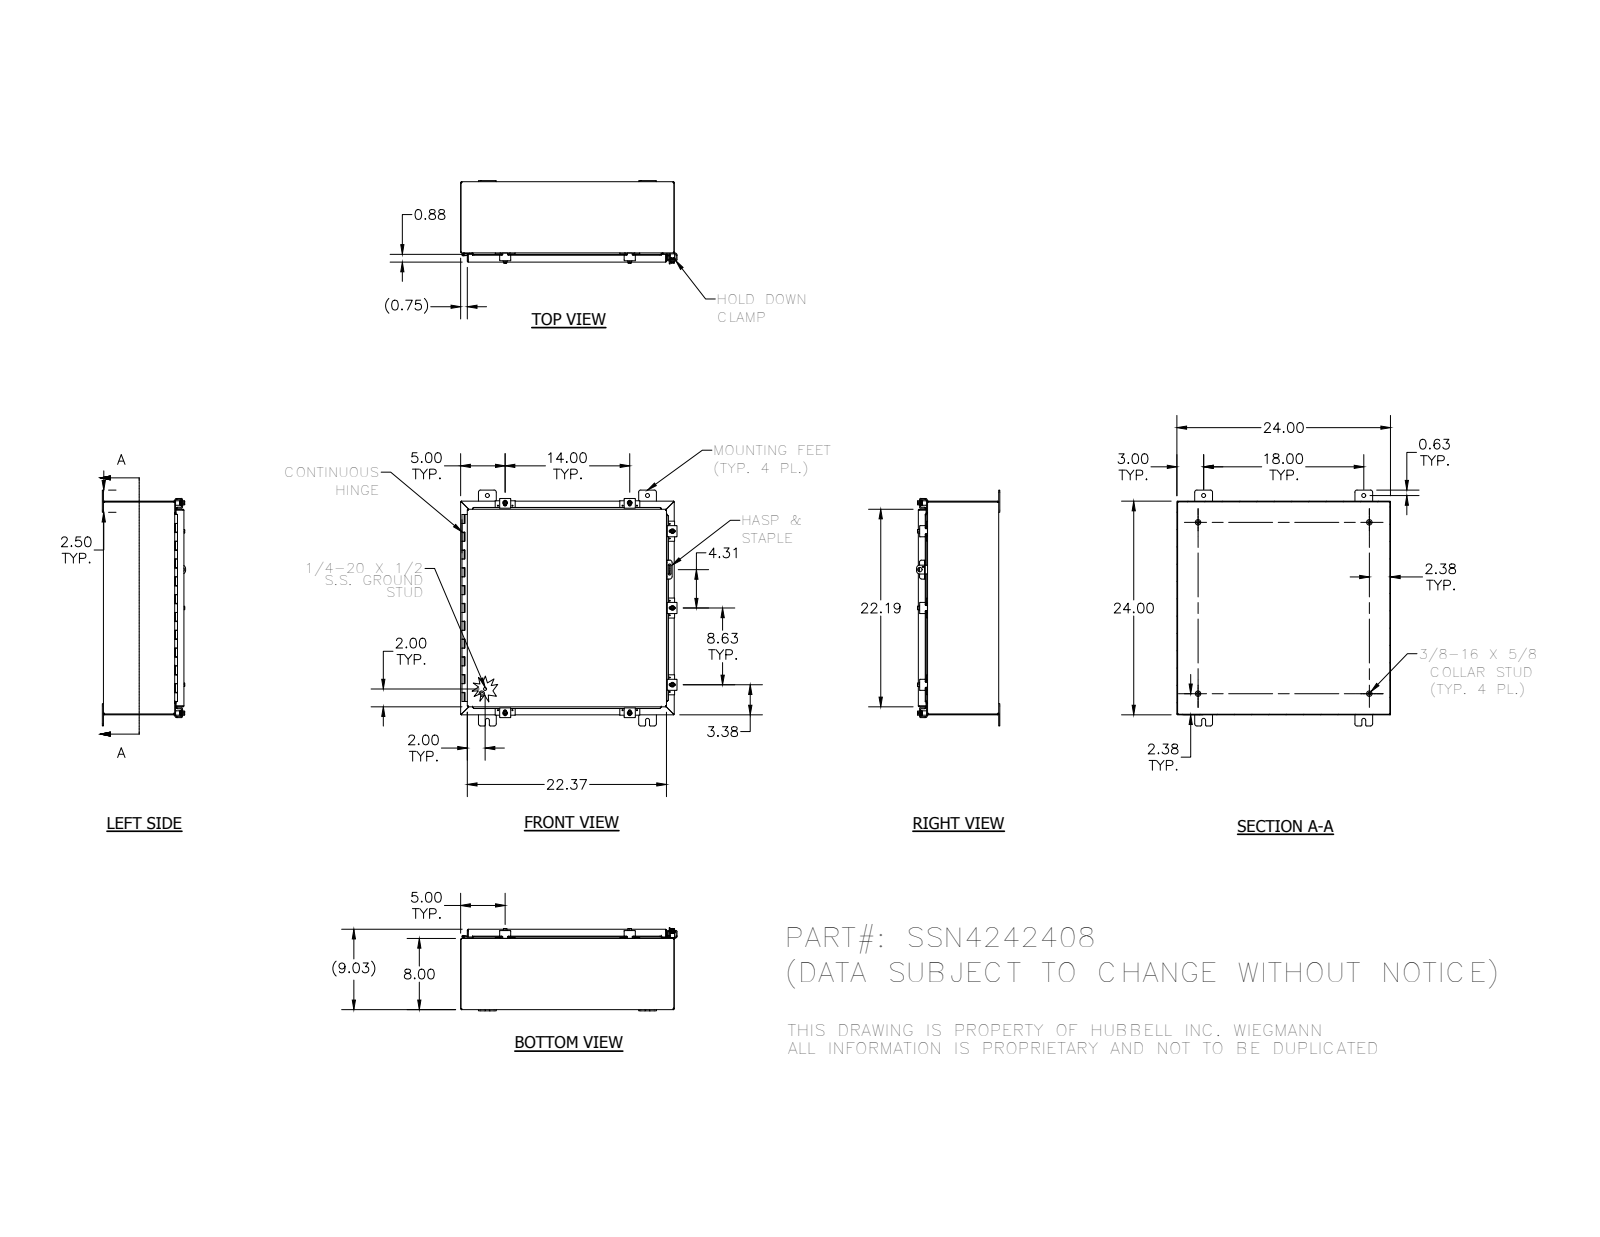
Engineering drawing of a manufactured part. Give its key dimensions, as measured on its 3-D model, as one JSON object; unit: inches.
{"part_name": "30824; 30824-1; 38859; 328138 (+8 more)", "step_written_by": "SolidWorks 2014 (AUTOMOTIVE_DESIGN)", "units": "inches", "bodies": {"solids": 52, "faces": 2042, "planar": 772, "cylindrical": 899, "other": 371}, "overall_size": [26.5, 24.311, 9.355], "volume_in3": 175.5, "surface_area_in2": 4603, "round_holes": [[0.11, 14], [0.211, 7], [0.281, 7], [0.3, 7], [0.438, 4], [0.125, 1], [0.156, 1], [0.5, 1]], "round_bosses_or_shafts": [[0.25, 9], [0.52, 7], [0.5, 7], [0.35, 7], [0.625, 4], [0.33, 4], [0.115, 2], [0.337, 1]], "partial_cylinders_radius": [[0.03, 83], [0.125, 37], [0.25, 33], [0.031, 23], [0.105, 23], [0.062, 15], [0.141, 14], [0.1, 10]], "face_to_face_distances": [0.074, 8.959, 23.926, 8.885, 9.033, 23.852, 24, 7.926, 1.033, 8], "hole_center_spacings": [0.876, 23.303, 14, 1.625, 13.191, 14.816, 19.639, 22.961]}
